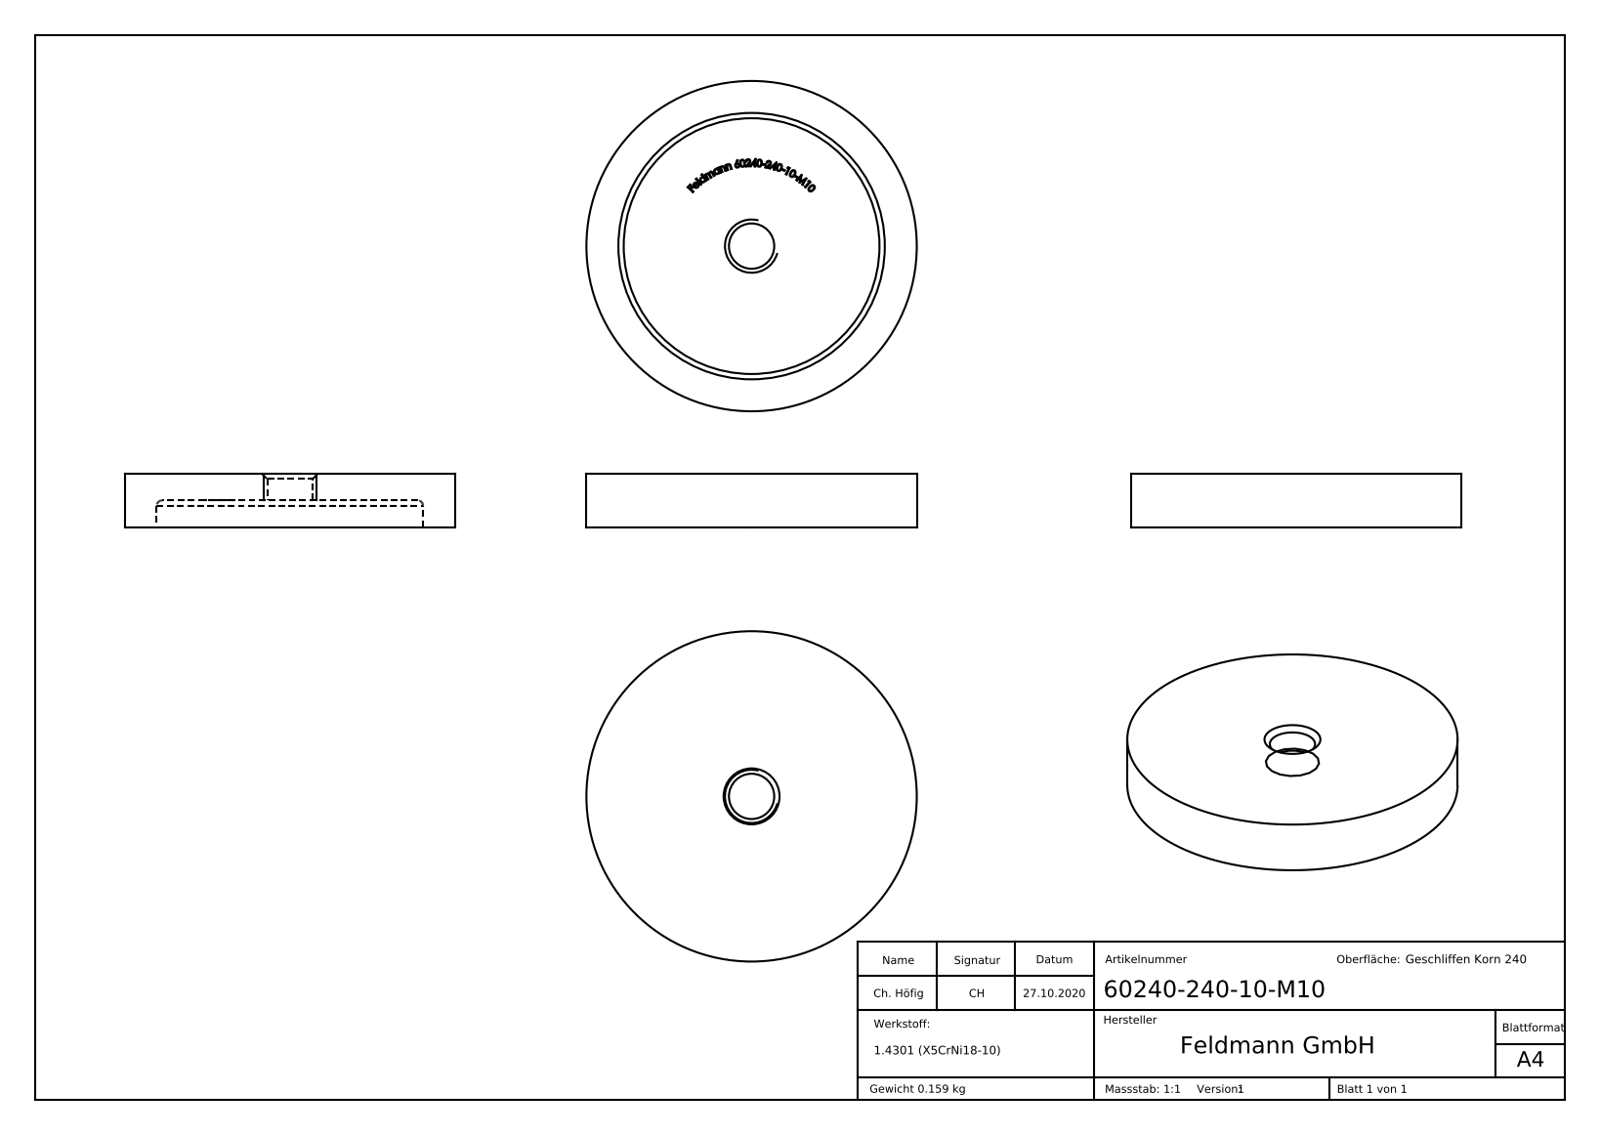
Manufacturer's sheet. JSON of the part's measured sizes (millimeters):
{"part_name": "60240-240-10-M10", "step_written_by": "SolidWorks 2018 (CONFIG_CONTROL_DESIGN)", "units": "millimeters", "bodies": {"solids": 1, "faces": 294, "planar": 170, "cylindrical": 6, "other": 118}, "overall_size": [62, 62, 10], "volume_mm3": 20108, "surface_area_mm2": 8722, "round_holes": [[8.5, 1], [50, 1]], "round_bosses_or_shafts": [[62, 1]], "face_to_face_distances": [5, 10, 5.1, 4.9, 0.54, 0.66, 0.85, 0.72, 0.67, 0.73]}
